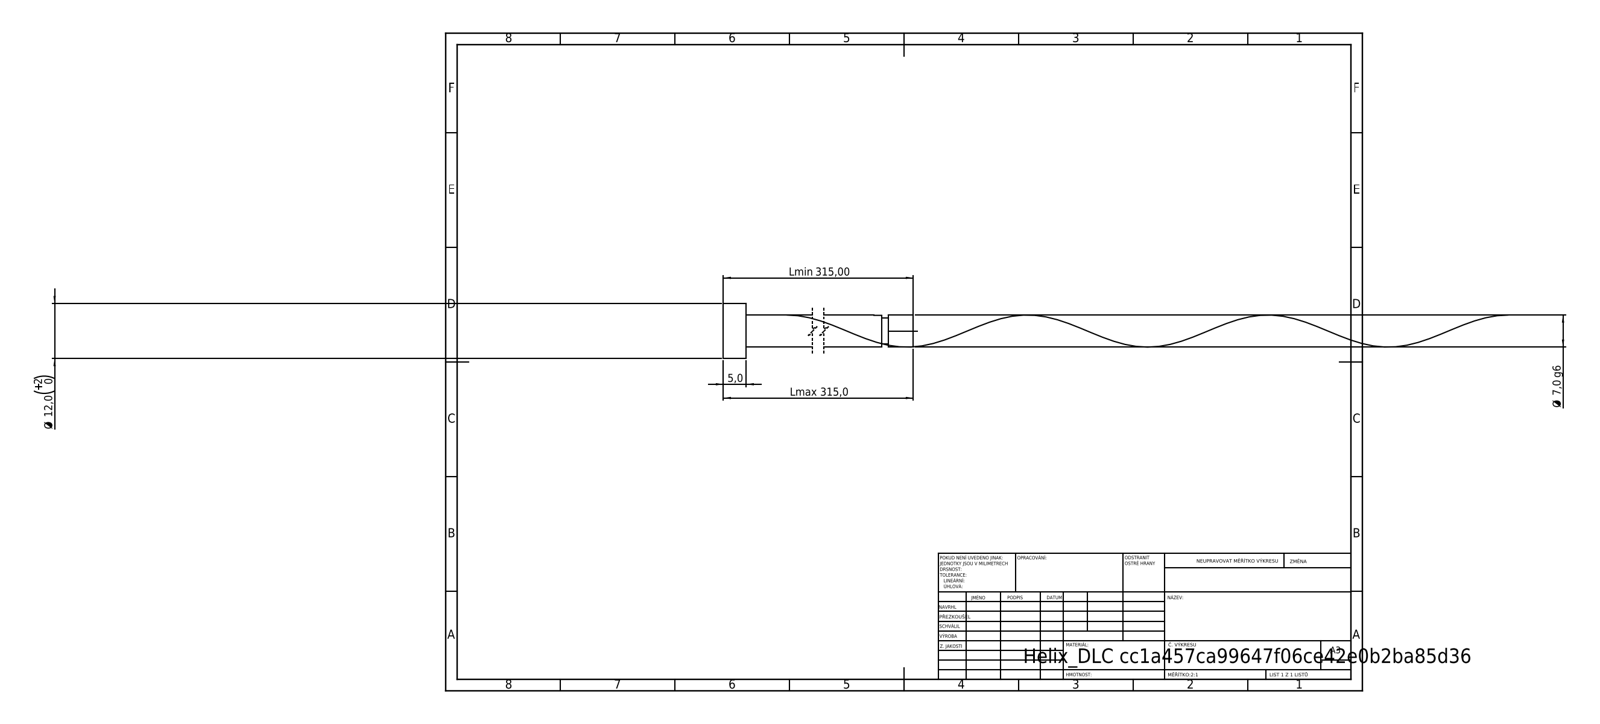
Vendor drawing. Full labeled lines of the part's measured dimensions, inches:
STEP written by: SolidWorks 2019 (CONFIG_CONTROL_DESIGN)
Units: inches
Bodies: 1 solid, 21 faces (6 planar, 14 cylindrical, 1 other)
Overall size (bounding box): 12.402 × 0.472 × 0.472
Volume: 0.754 in³ · Surface area: 11.42 in²
Round bosses / shafts (diameter × count): ⌀0.472 ×1, ⌀0.276 ×1, ⌀0.22 ×1
Main face-to-face distances: 0.197, 12.402, 12.205, 12.185, 11.988, 0.217, 12.13, 11.933, 0.055, 0.272
